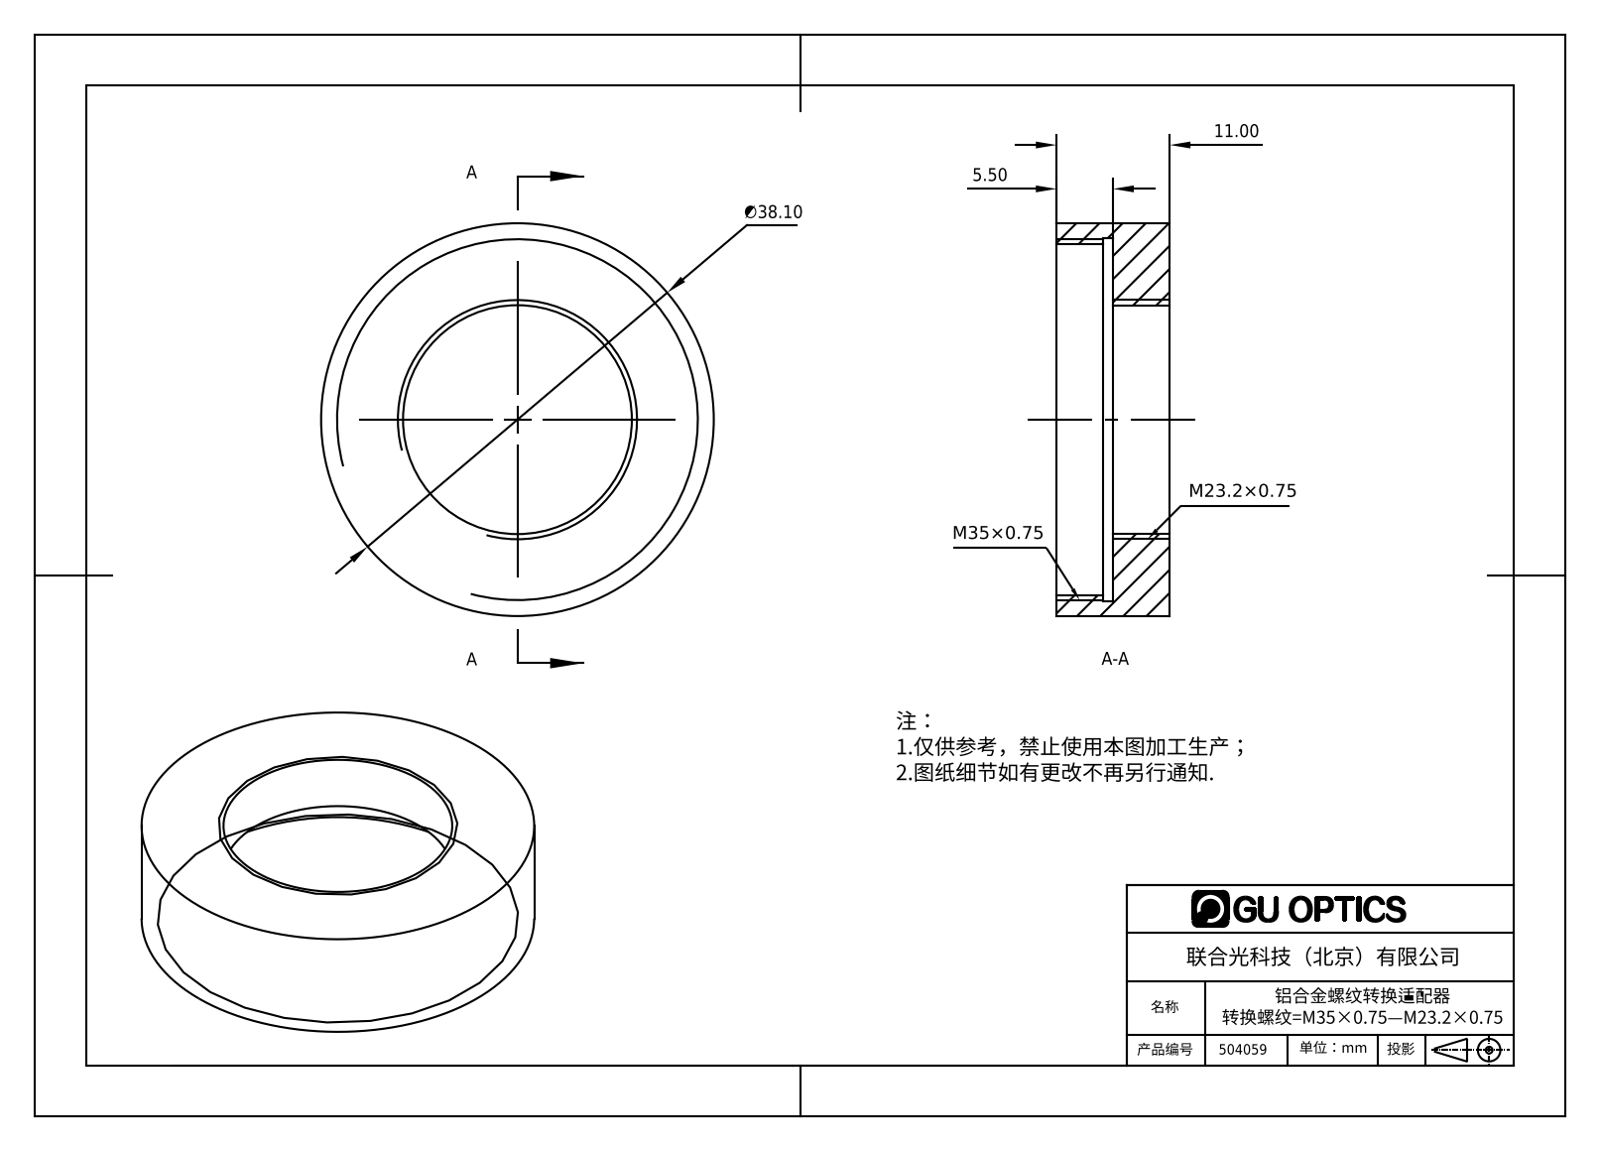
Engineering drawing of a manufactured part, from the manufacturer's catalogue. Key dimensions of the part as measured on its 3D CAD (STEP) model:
Part name (STEP PRODUCT): 504059
STEP written by: SolidWorks 2016 (AUTOMOTIVE_DESIGN)
Units: millimetres
Bodies: 1 solid, 12 faces (4 planar, 8 cylindrical, 0 other)
Overall size (bounding box): 38.1 × 38.1 × 11
Volume: 5 353 mm³ · Surface area: 3 928 mm²
Round holes (diameter × count): ⌀22.2 ×1, ⌀34 ×1, ⌀35.2 ×1
Round bosses / shafts (diameter × count): ⌀38.1 ×1
Main face-to-face distances: 5.5, 11, 4.5, 1, 6.5
